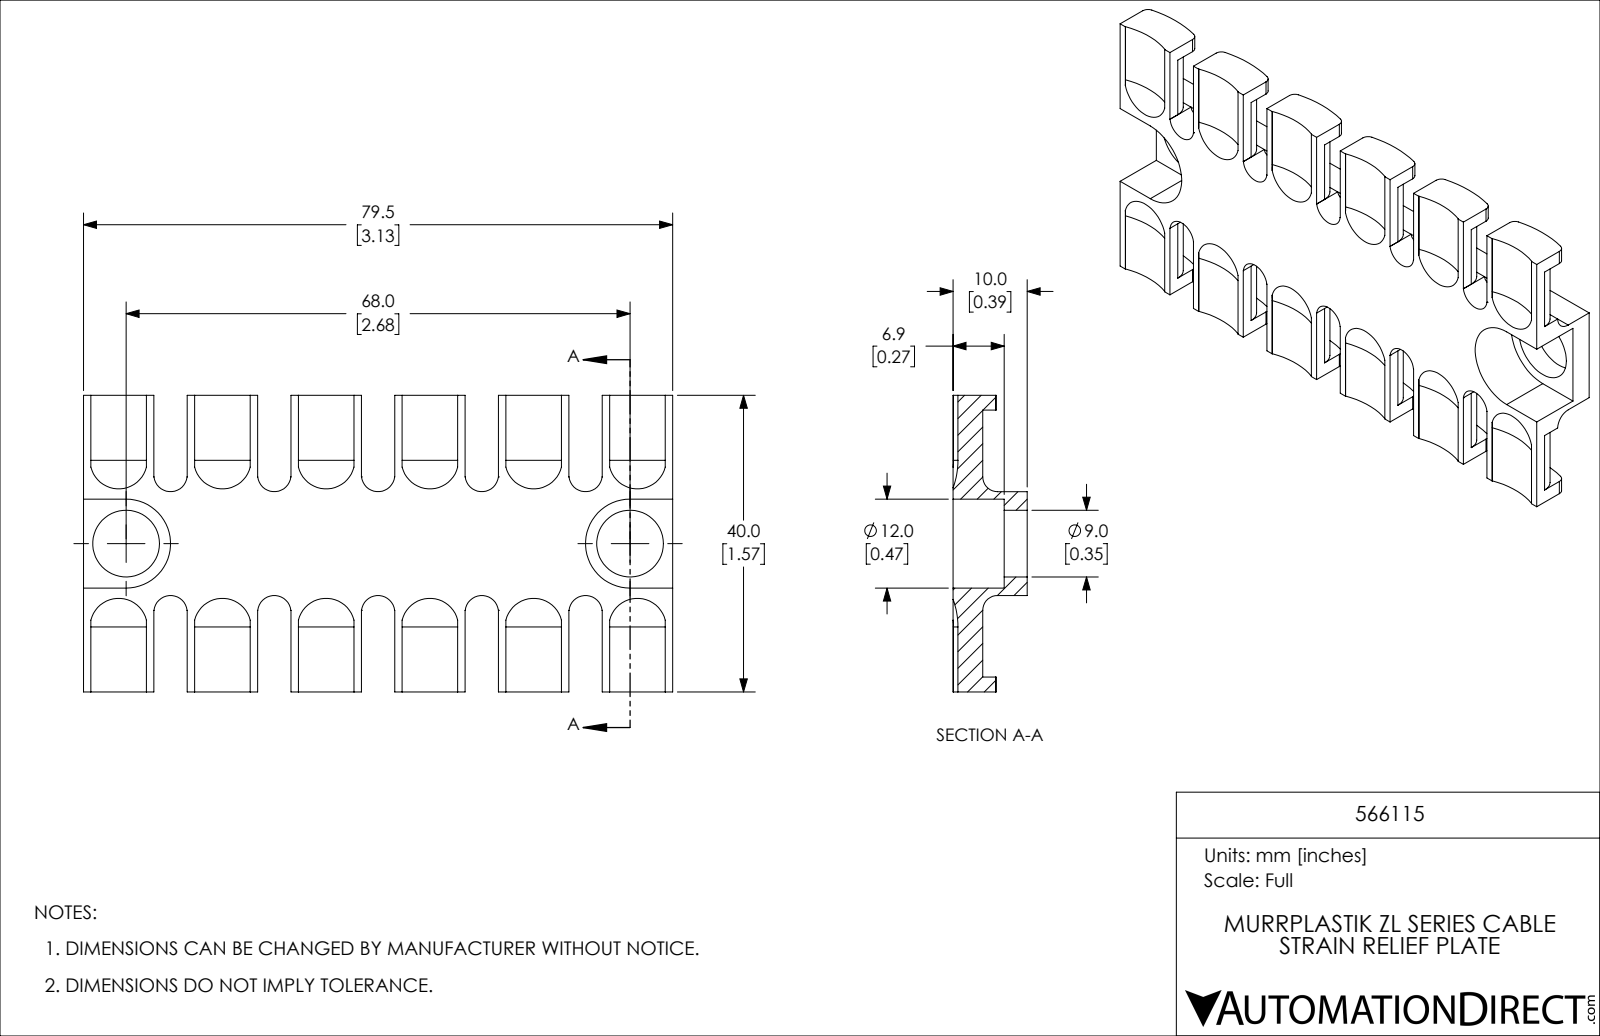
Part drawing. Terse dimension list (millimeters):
name: 566115
written by: SolidWorks 2019 (CONFIG_CONTROL_DESIGN)
unit: mm
bodies: 1 solid, 258 faces (124 planar, 122 cylindrical, 12 other)
size: 79.5 × 40 × 10
volume: 12 180 mm³; area: 9 420 mm²
holes: 2× ⌀9
rounds: 12× R1, 12× R2.5, 10× R2.25, 6× R11, 6× R16, 2× R2, 2× R6, 2× R7
face distances: 14, 4, 11, 13, 24, 10, 3, 16, 27, 6
hole spacings: 68
